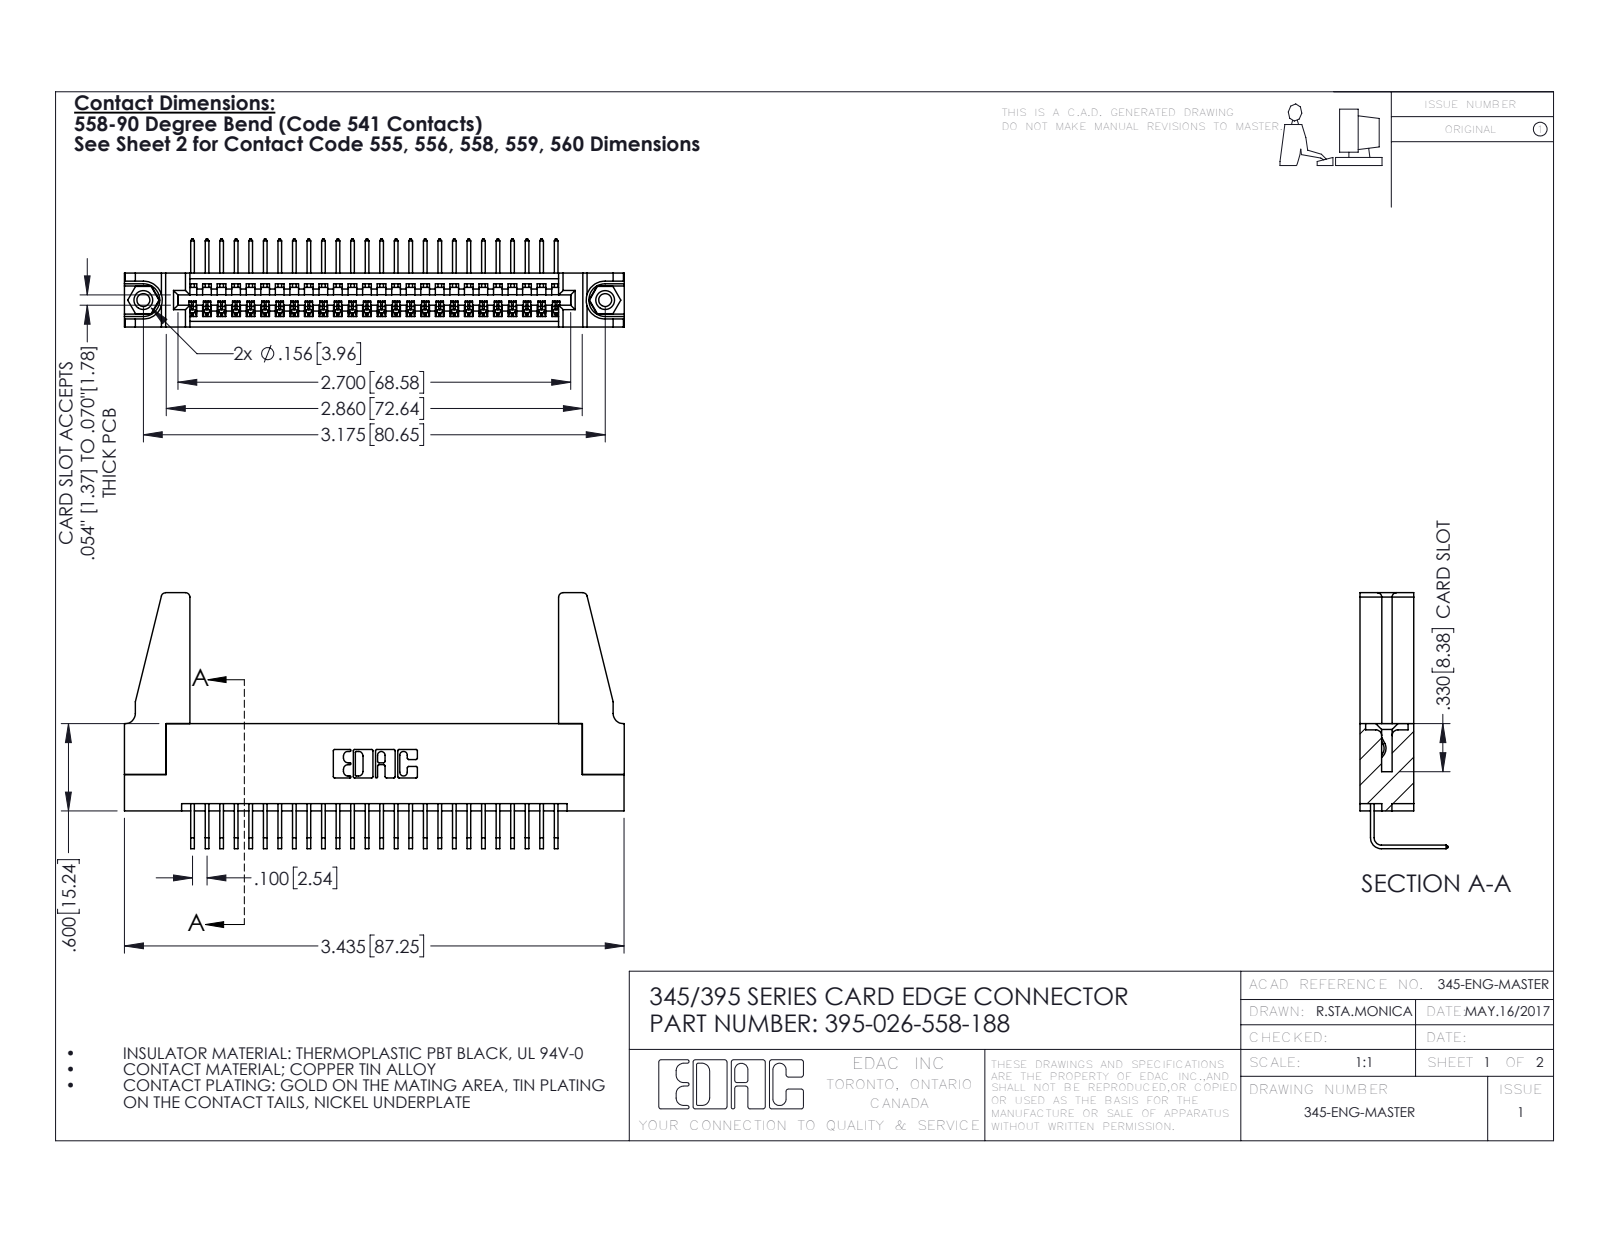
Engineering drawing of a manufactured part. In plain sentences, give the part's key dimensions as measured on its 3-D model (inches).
The part is named "345-250-001_345-250-001-102; 395-026-558-188; 345-220-078_345-220-088; 345 Part_Flush Mounting Lugs - 0.156 Dia-TH (+1 more)". Its 3-D file was written by "SolidWorks 2016 (CONFIG_CONTROL_DESIGN)". It is 31 solids with 1810 faces: 1244 planar, 550 cylindrical and 16 other. Overall it measures 3.436 by 1.759 by 0.605 inches. Its volume is 0.702 cubic inches and its surface area 22.29 square inches. Round holes: 2 of diameter 0.089, 2 of diameter 0.125, 2 of diameter 0.156, 1 of diameter 0.064. Round bosses or shafts: 2 of diameter 0.155. Partial cylindrical surfaces (rounded edges, fillets, slot ends): 52 of radius 0.006, 22 of radius 0.01, 8 of radius 0.03, 6 of radius 0.007, 6 of radius 0.031, 3 of radius 0.026, 2 of radius 0.031, 2 of radius 0.04. The main face-to-face distances are 0.072, 0.37, 0.298, 0.2, 0.098, 0.272, 0.025, 0.225, 0.149, 0.148. The hole center spacings are 0.27, 2.94, 3.175.
